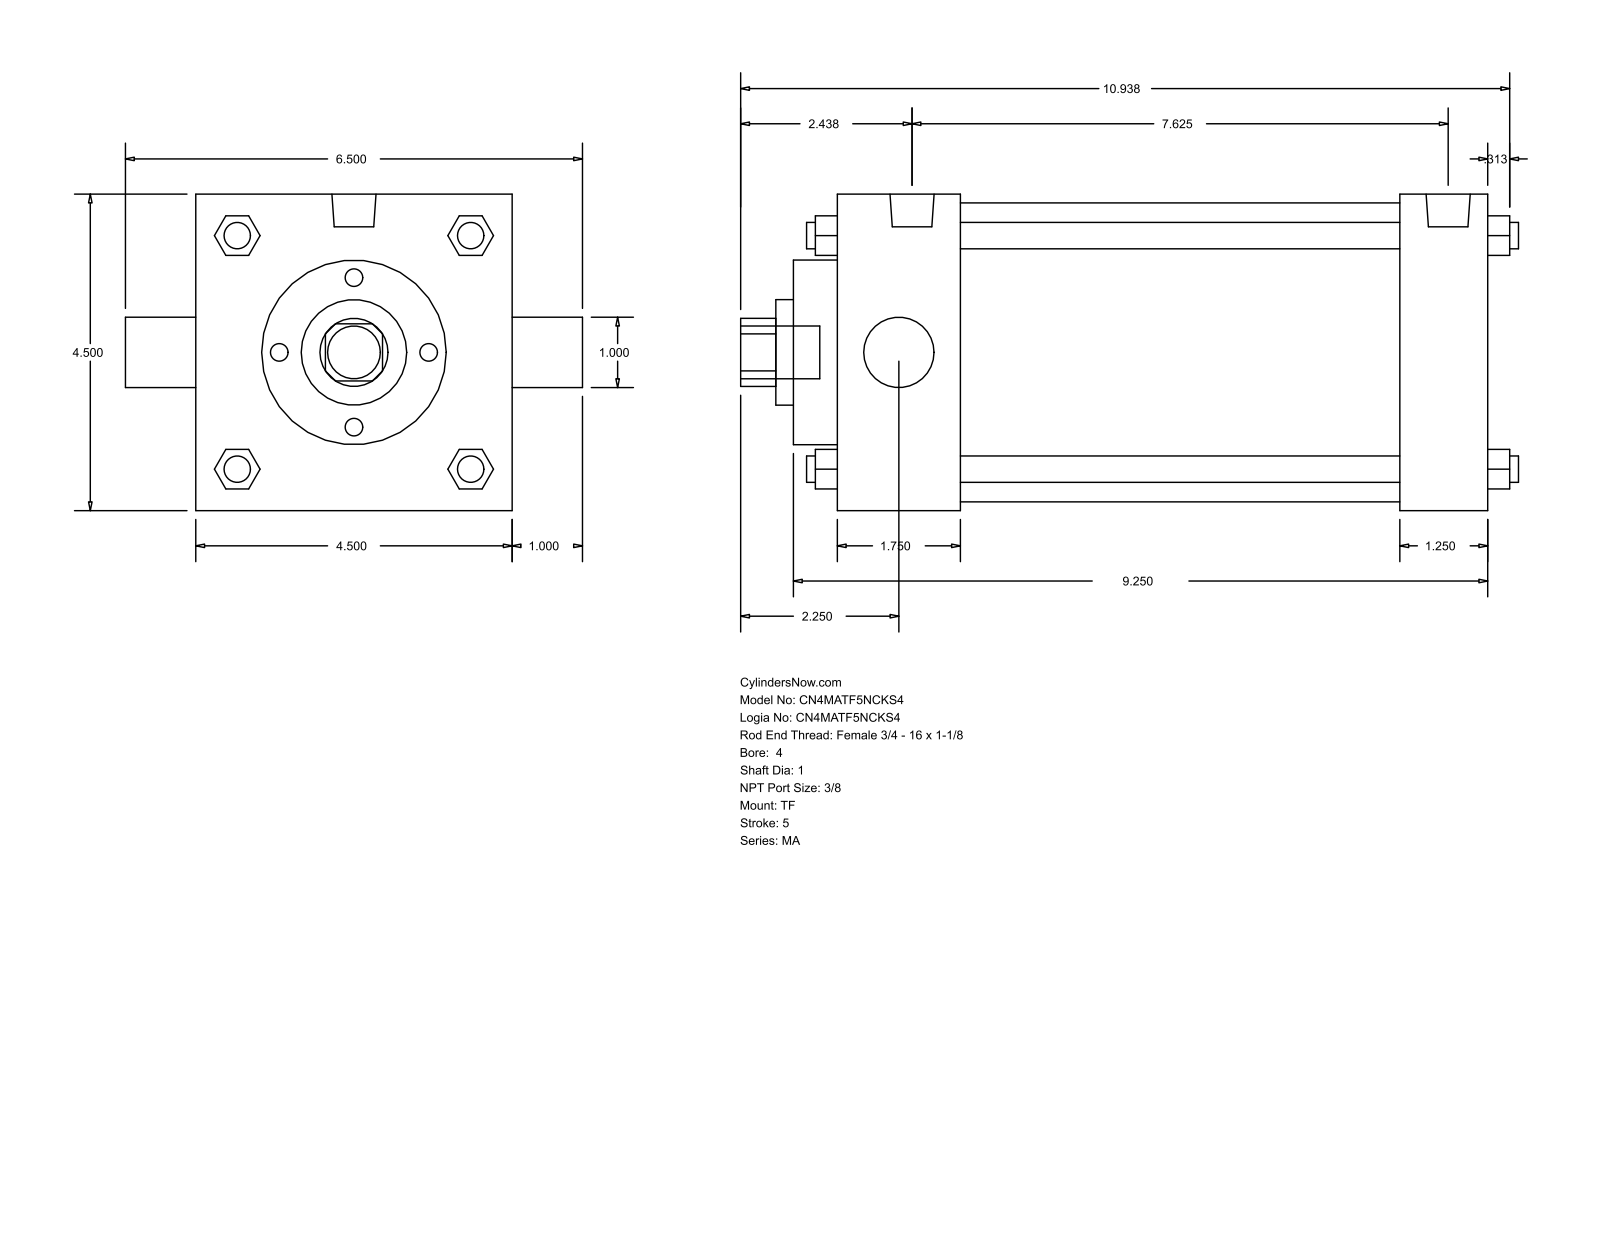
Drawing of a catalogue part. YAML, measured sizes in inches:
part_name: "MA_TF__0400_1"
step_written_by: "GSSL Pune (CONFIG_CONTROL_DESIGN)"
units: inches
bodies: {solids: 0, faces: 122, planar: 93, cylindrical: 29, other: 0}
overall_size: [11.063, 6.5, 4.5]
round_holes:
  - {diameter: 1, count: 2}
  - {diameter: 1.5, count: 1}
  - {diameter: 2.625, count: 1}
  - {diameter: 4.25, count: 1}
round_bosses_or_shafts:
  - {diameter: 0.375, count: 4}
  - {diameter: 0.437, count: 3}
  - {diameter: 0.627, count: 2}
  - {diameter: 0.75, count: 1}
partial_cylinders:
  - {radius: 0.484, count: 1}
face_to_face_distances: [4.5, 9.25, 8, 1.25, 1.75, 6.25, 7.5, 0.625, 2.375, 8.625]
